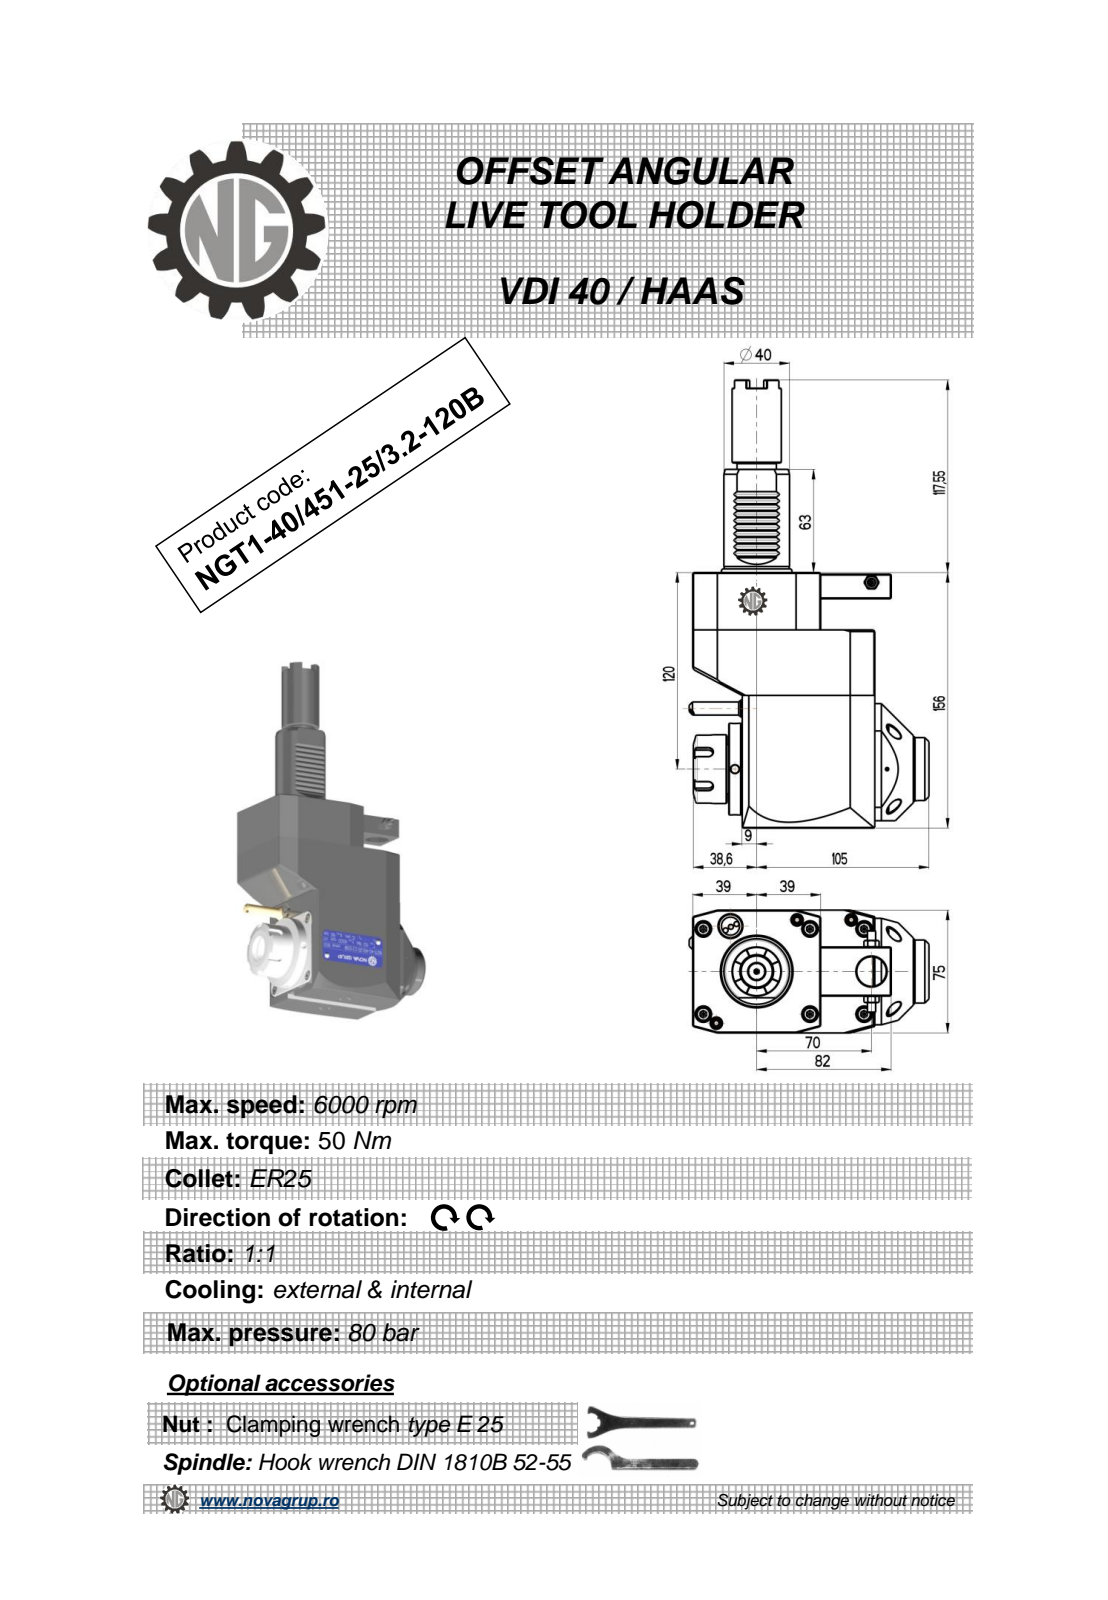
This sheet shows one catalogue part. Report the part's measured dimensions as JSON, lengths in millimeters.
{"part_name": "NGT1_40_451_25_3_2_120B", "step_written_by": "PRO/ENGINEER BY PARAMETRIC TECHNOLOGY CORPORATION, 2010280 (CONFIG_CONTROL_DESIGN)", "units": "millimeters", "bodies": {"solids": 1, "faces": 479, "planar": 230, "cylindrical": 91, "other": 158}, "overall_size": [273.55, 146.14, 75], "volume_mm3": 1246000, "surface_area_mm2": 96161, "round_holes": [[5, 3], [3, 1], [4.2, 1], [9.5, 1], [18, 1], [20.3, 1]], "round_bosses_or_shafts": [[56, 1], [43, 1], [42, 1], [40, 1], [38.5, 1], [33, 1], [30, 1], [24, 1]], "partial_cylinders_radius": [[0.26, 12], [0.3, 10], [0.2, 6], [3, 5], [0.5, 1], [10, 1], [40, 1]], "face_to_face_distances": [75, 156, 111, 121, 33, 30, 35, 81, 93.43, 78], "hole_center_spacings": [40.93, 77.5, 83.25, 112.5, 141.16]}
